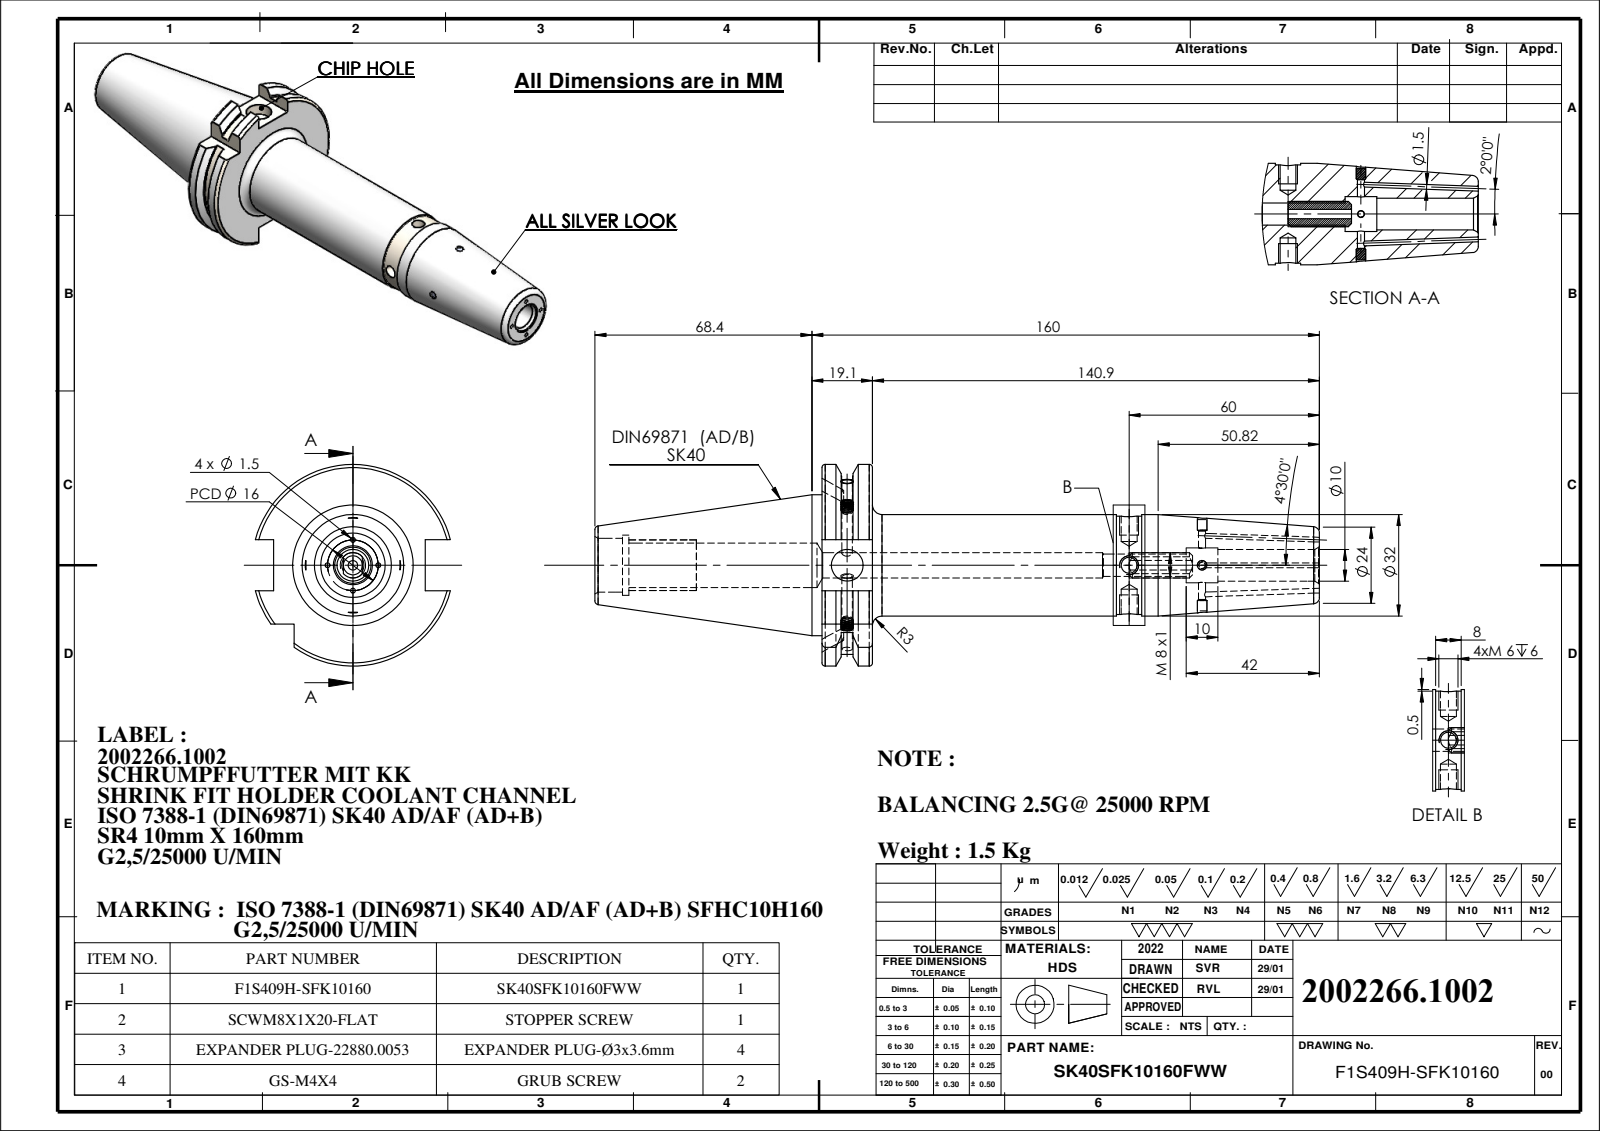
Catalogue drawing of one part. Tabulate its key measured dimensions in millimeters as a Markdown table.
| quantity | value |
| --- | --- |
| part name | GS-M4X4_DIN 913 - M4 x 4-N; SK40SFK10160FWW; SCWM8X1X20-FLAT; EXPANDER PLUG Ø3x3.6 (+1 more) |
| STEP written by | SolidWorks 2018 (CONFIG_CONTROL_DESIGN) |
| units | millimeters |
| bodies | 8 solids, 293 faces (62 planar, 105 cylindrical, 126 other) |
| overall size | 228.4 × 63.55 × 61.48 |
| volume | 195 307 mm³ |
| surface area | 40 577 mm² |
| round holes (diameter × count) | 1.5 × 4, 3 × 3, 2.2 × 2, 5 × 2, 3.3 × 1, 7 × 1, 9.99 × 1, 10 × 1, 10.99 × 1, 14 × 1, 17 × 1, 19 × 1 |
| round bosses / shafts (diameter × count) | 4 × 2, 44.45 × 1, 32 × 1, 31 × 1, 8 × 1 |
| partial cylindrical surfaces (radius × count) | 28.12 × 1, 31.77 × 1 |
| main face-to-face distances | 15.9, 156.8, 140.9, 16.1, 47.8, 22, 71.6, 87.5, 228.4, 10.7 |
| hole center spacings | 23, 88.85, 111.85 |
